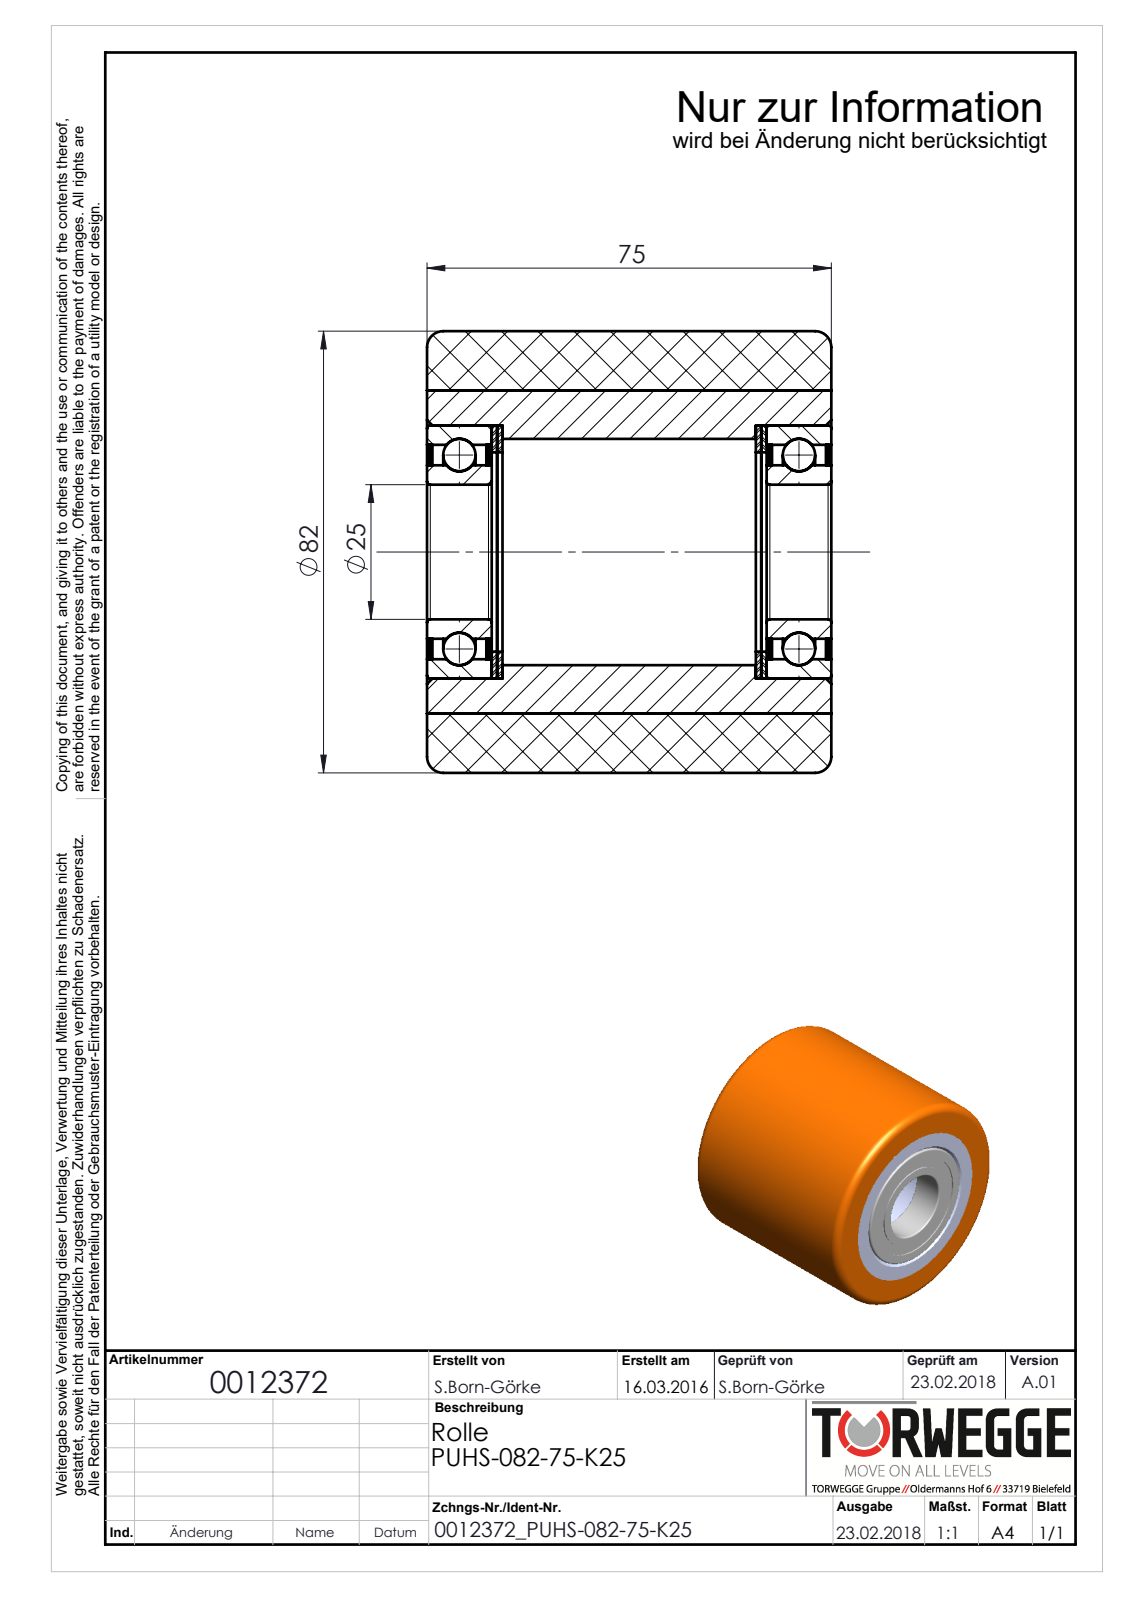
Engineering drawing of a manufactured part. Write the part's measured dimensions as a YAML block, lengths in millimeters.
part_name: "0012372_PUHS-082-75-K25"
step_written_by: "SolidWorks 2016 (AUTOMOTIVE_DESIGN)"
units: millimeters
bodies: {solids: 16, faces: 158, planar: 30, cylindrical: 68, other: 60}
overall_size: [82, 82, 75]
volume: 308742
surface_area: 93450
round_holes:
  - {diameter: 25, count: 1}
  - {diameter: 32.2, count: 1}
  - {diameter: 37, count: 1}
  - {diameter: 39.8, count: 1}
  - {diameter: 42, count: 1}
  - {diameter: 60, count: 1}
round_bosses_or_shafts:
  - {diameter: 82, count: 1}
  - {diameter: 47, count: 1}
face_to_face_distances: [1, 63, 12, 0.5, 13, 62, 50, 75, 49, 61]
